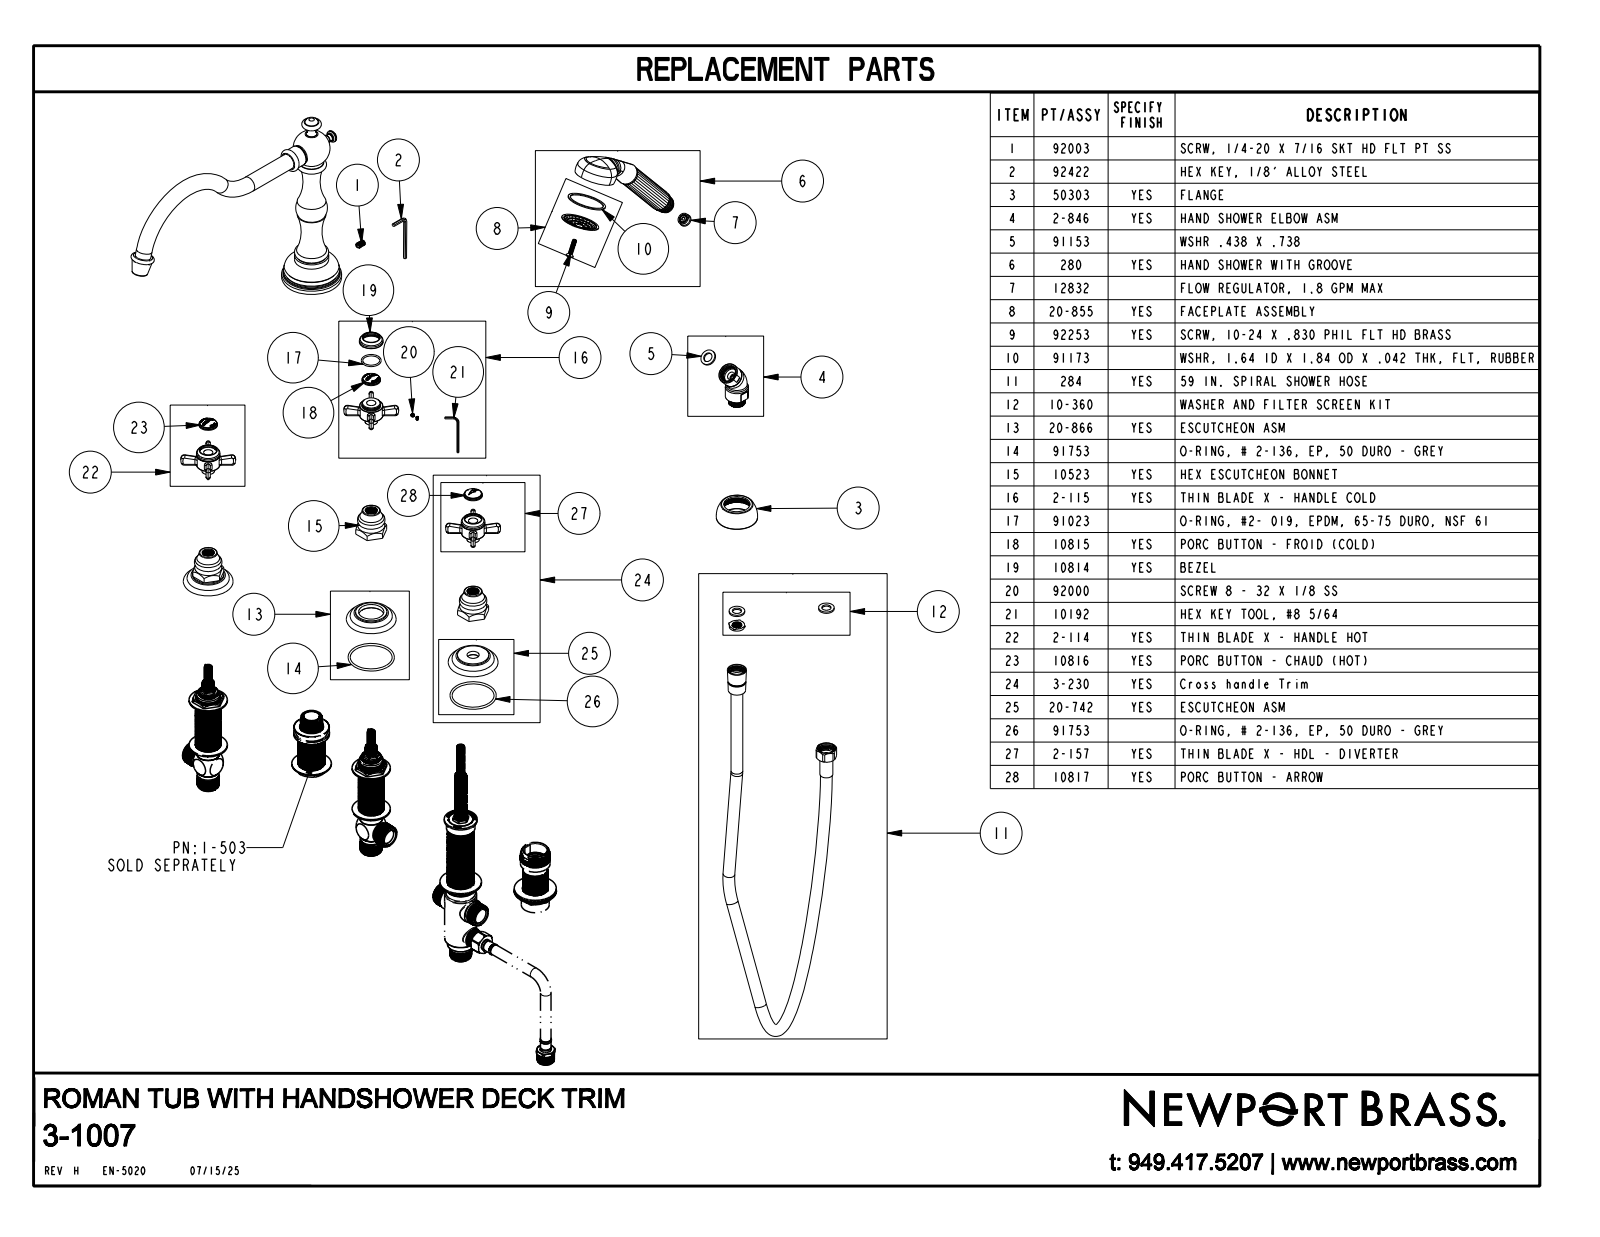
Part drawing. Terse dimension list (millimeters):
name: 3-1007_SW0003
written by: CREO PARAMETRIC BY PTC INC, 2018400 (CONFIG_CONTROL_DESIGN)
unit: mm
bodies: 5 solids, 1694 faces (535 planar, 511 cylindrical, 648 other)
size: 614 × 340.2 × 247.5
volume: 694 200 mm³; area: 127 100 mm²
holes: 52× ⌀1.2, 3× ⌀20.7
bosses: 4× ⌀25.1, 3× ⌀37.6, 3× ⌀28.3, 3× ⌀27.9, 3× ⌀15.3, 2× ⌀19.1, 1× ⌀72.1, 1× ⌀67.7
rounds: 37× R2.5, 28× R0.3, 17× R0.6, 14× R0.2, 10× R0.1, 10× R0.4, 8× R0.2, 8× R0.4
face distances: 5.1, 51.6, 33.4, 143.7, 107.7, 251.4, 9.5, 42.1, 307.9, 132
hole spacings: 9.3, 12.6, 4.7, 4.7, 4.7, 4.7, 9, 13.6
